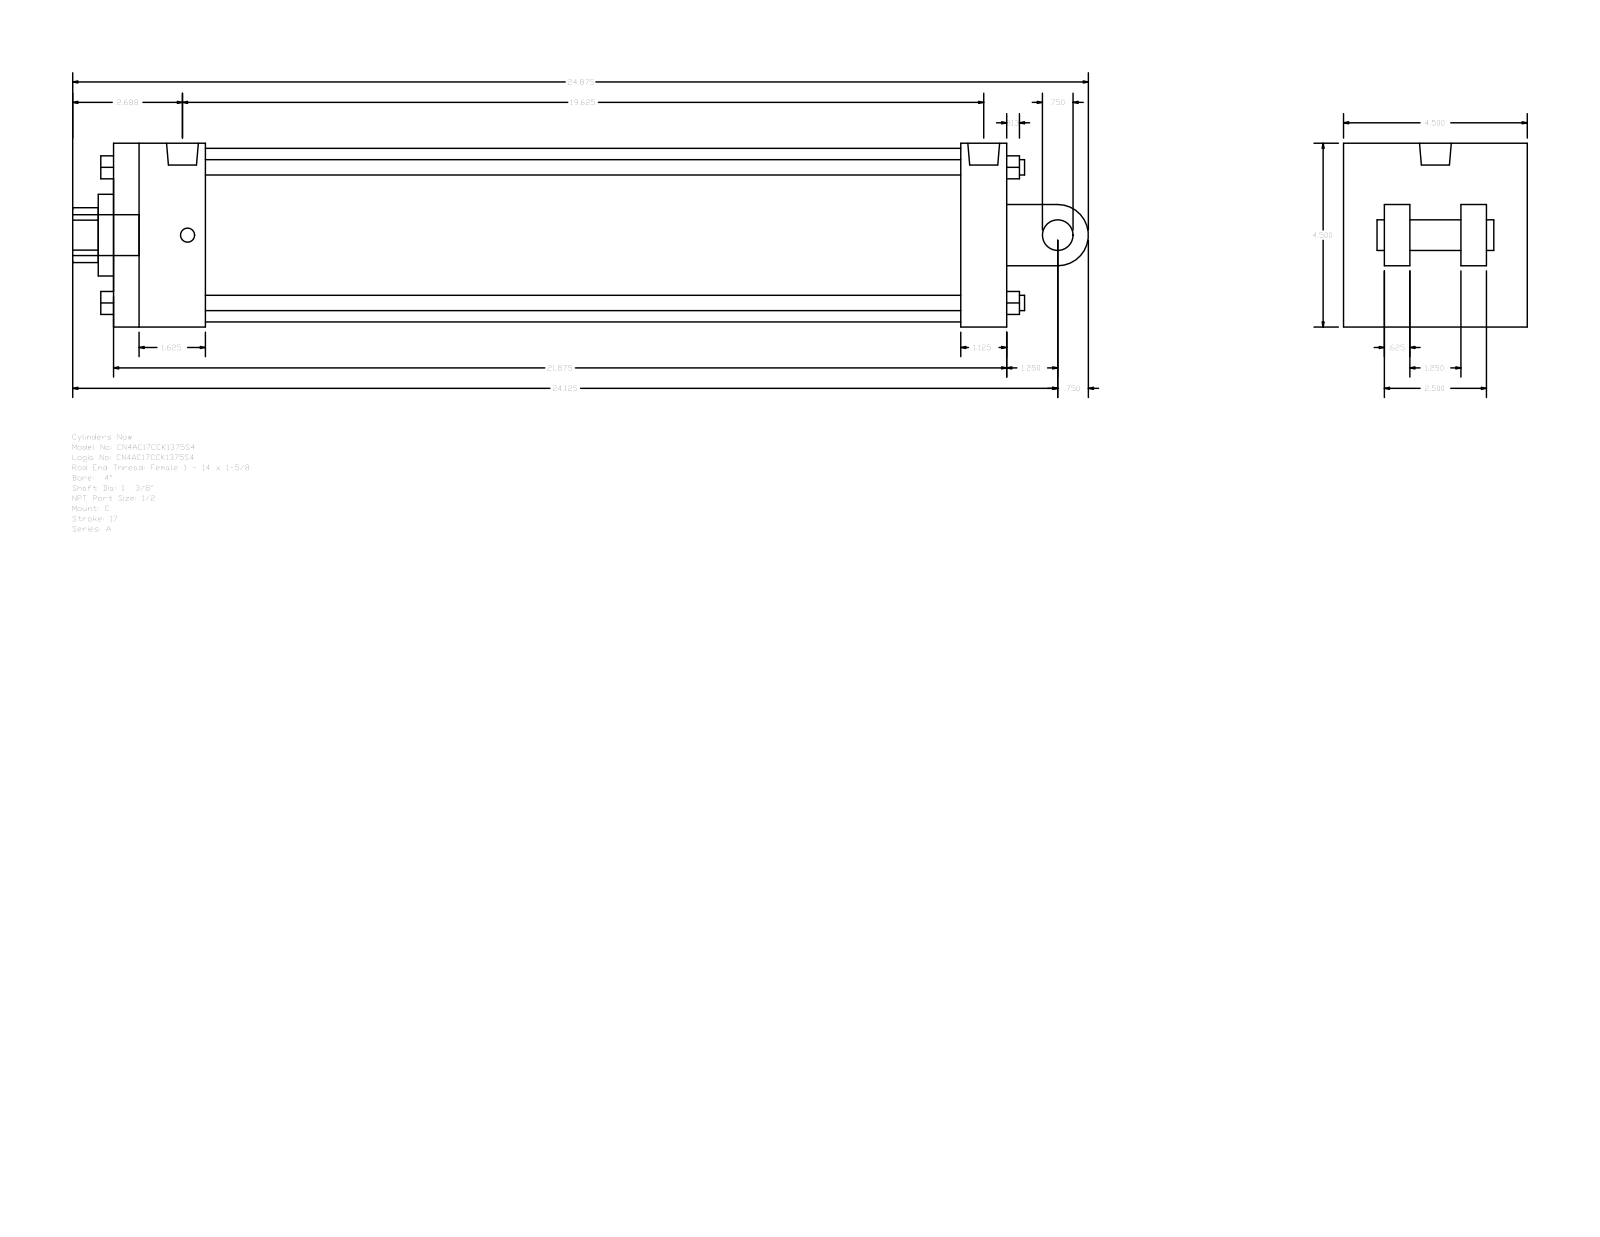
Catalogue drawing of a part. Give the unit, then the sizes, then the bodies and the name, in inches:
Units: inches
Overall size (bounding box): 24.875 × 4.5 × 4.5
Round holes (diameter × count): ⌀0.344 ×2, ⌀0.778 ×1, ⌀1.375 ×1, ⌀2 ×1, ⌀4.25 ×1
Round bosses / shafts (diameter × count): ⌀0.375 ×4, ⌀0.344 ×2, ⌀1 ×1, ⌀0.778 ×1, ⌀0.75 ×1
Partial cylindrical surfaces — rounded edges, fillets, slot ends (radius × count): R0.672 ×1, R0.75 ×1
Main face-to-face distances: 4.5, 21.875, 2.875, 1.125, 20.75, 2.25, 18.5, 19.625, 0.625, 1.625
Hole centre spacings: 0.125
Bodies: 0 solids, 135 faces (102 planar, 33 cylindrical, 0 other)
Part name (STEP PRODUCT): A_C__0400_1.375
STEP written by: GSSL Pune (CONFIG_CONTROL_DESIGN)
